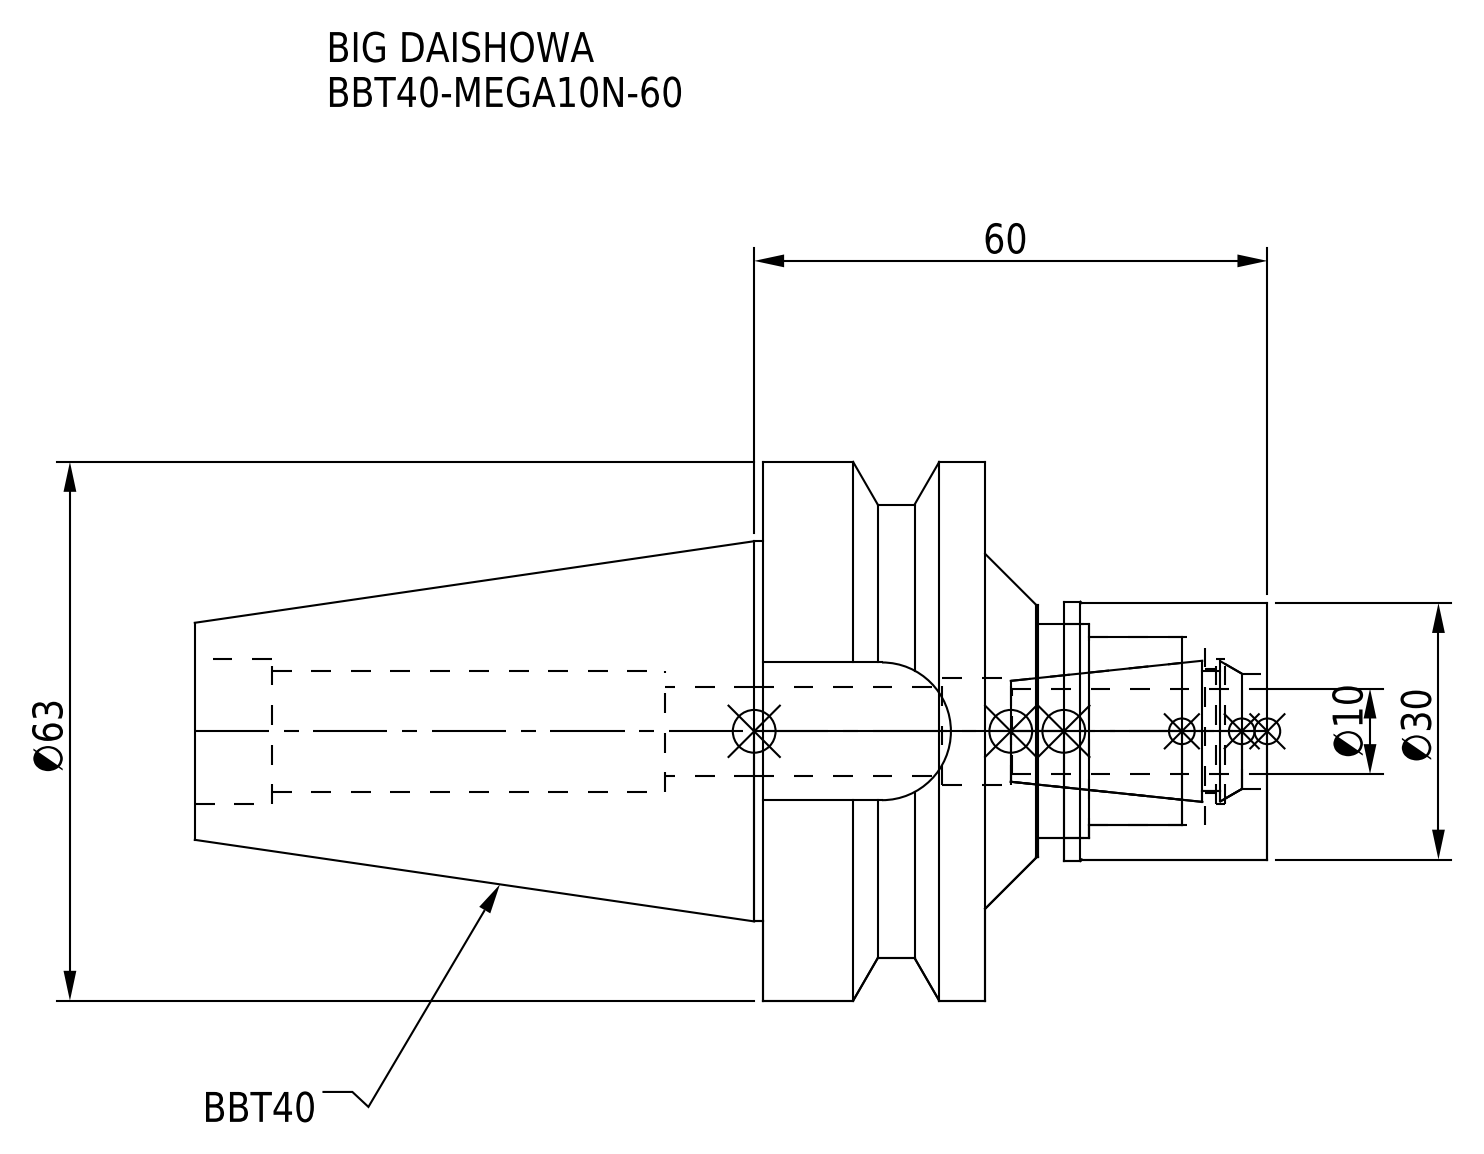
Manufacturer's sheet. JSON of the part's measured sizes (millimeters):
{"part_name": "BBT40-MEGA10N-60-100.stp; BBT40-MEGA10N-60-100-FreeParts; DXF_TEMP_ASSY_ASM_4_ASM.stp; MGN10_1.stp (+3 more)", "step_written_by": "SolidWorks 2019 (CONFIG_CONTROL_DESIGN)", "units": "millimeters", "bodies": {"solids": 2, "faces": 76, "planar": 22, "cylindrical": 40, "other": 14}, "overall_size": [125.4, 63, 63], "volume_mm3": 141679, "surface_area_mm2": 29850, "round_holes": [[10.4, 1], [10.41, 1], [12.5, 1], [13.5, 1], [14.2, 1], [14.5, 1], [17, 1], [22, 1], [25, 1]], "round_bosses_or_shafts": [[63, 1], [53, 1], [44.45, 1], [30.3, 1], [30, 1], [29.5, 1]], "partial_cylinders_radius": [[8.05, 1]], "face_to_face_distances": [26, 33, 59, 45, 125.4, 92.4, 66.4, 23.8, 9.2, 35.2]}
